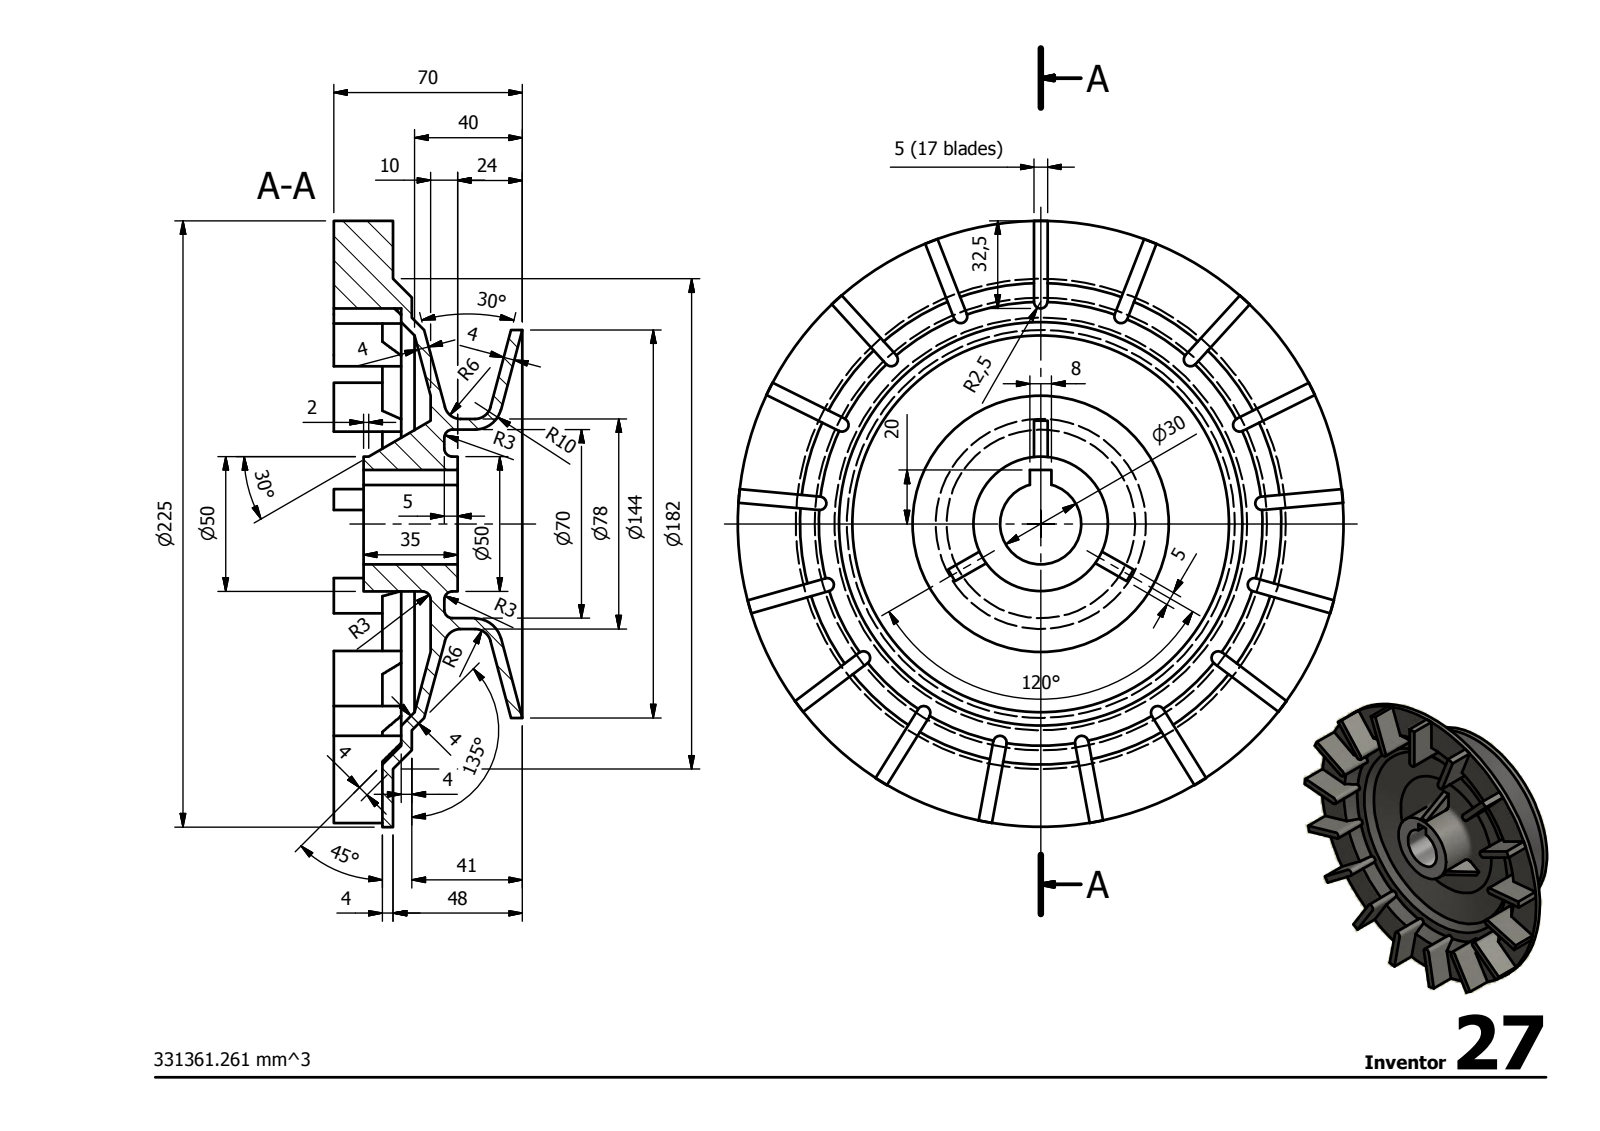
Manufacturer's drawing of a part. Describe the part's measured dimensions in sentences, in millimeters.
Its 3-D file was written by "Autodesk Inventor 2014 (AUTOMOTIVE_DESIGN)". It is 1 solid with 160 faces: 87 planar, 41 cylindrical and 32 other. Overall it measures 225 by 225 by 70 millimeters. Its volume is 331 348 cubic millimeters and its surface area 151 204 square millimeters. Round holes: 1 of diameter 30, 1 of diameter 70. Round bosses or shafts: 1 of diameter 225, 1 of diameter 144, 1 of diameter 78, 1 of diameter 50. Partial cylindrical surfaces (rounded edges, fillets, slot ends): 17 of radius 2.5, 17 of radius 110.8. The main face-to-face distances are 4, 7, 11, 18, 14, 5, 4.99, 25, 3, 5.01.
